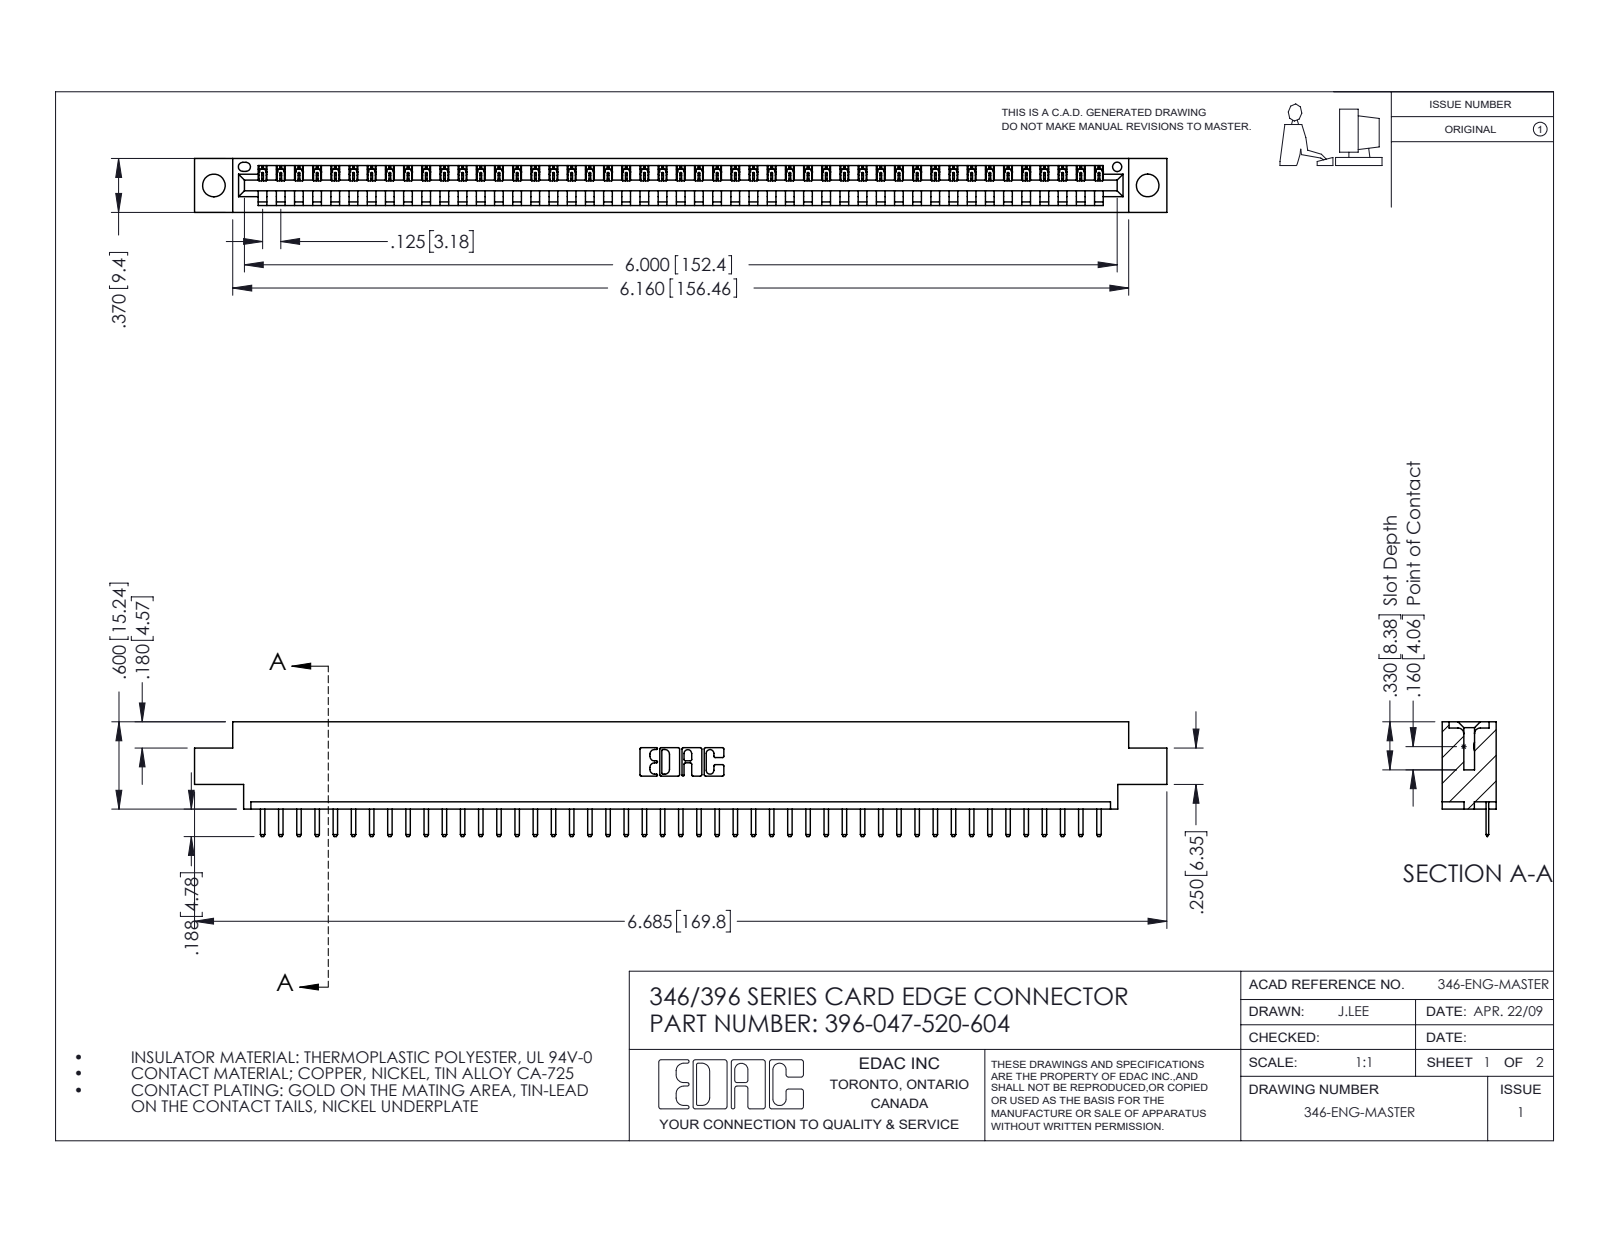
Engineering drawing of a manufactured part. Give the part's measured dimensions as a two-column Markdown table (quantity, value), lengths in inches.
| quantity | value |
| --- | --- |
| part name | 345-292-001_345-293-120; 396-047-520-604; 346 Part_0.170 Offset - 0.156 Dia-TH |
| STEP written by | SolidWorks 2016 (CONFIG_CONTROL_DESIGN) |
| units | inches |
| bodies | 48 solids, 3040 faces (2054 planar, 986 cylindrical, 0 other) |
| overall size | 6.685 × 0.788 × 0.37 |
| volume | 0.971 in³ |
| surface area | 30.15 in² |
| round holes (diameter × count) | 0.156 × 2, 0.064 × 1 |
| partial cylindrical surfaces (radius × count) | 0.01 × 96, 0.006 × 94, 0.01 × 22, 0.007 × 6, 0.031 × 6, 0.026 × 3, 0.031 × 2, 0.04 × 2 |
| main face-to-face distances | 0.048, 0.322, 0.37, 0.25, 0.148, 0.222, 0.1, 0.174, 0.072, 0.298 |
| hole center spacings | 0.246, 6.211, 6.42 |
